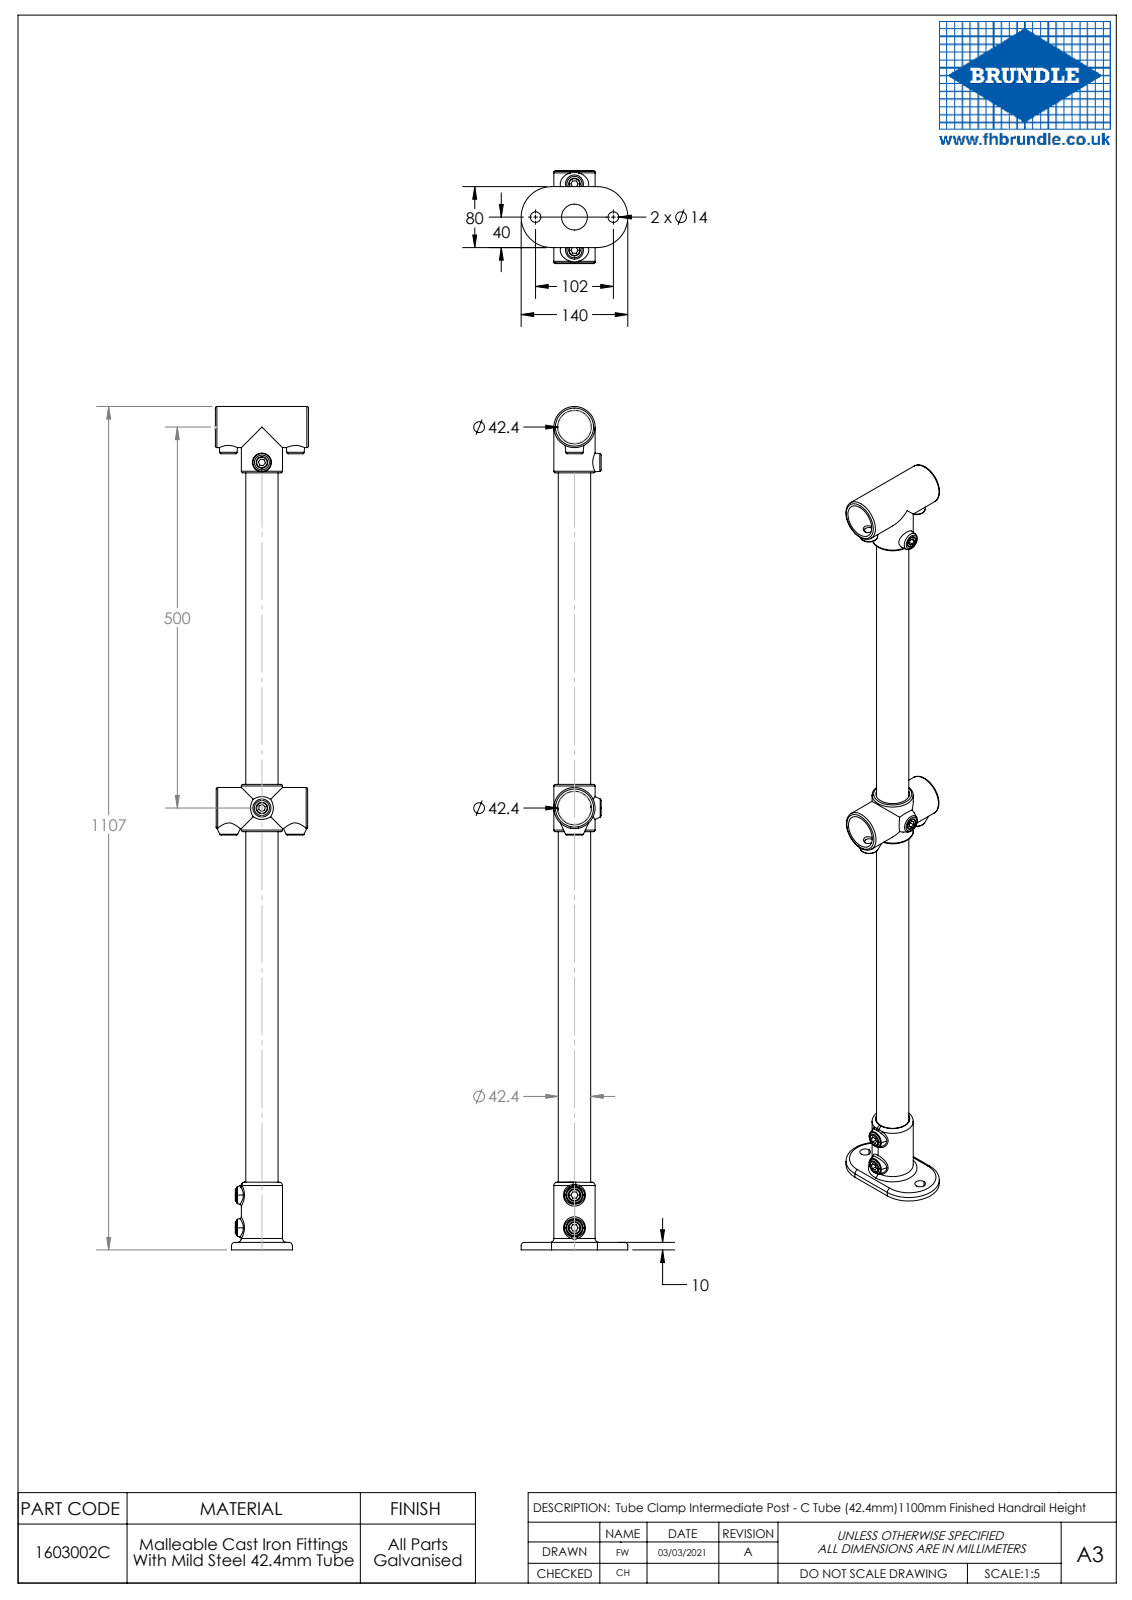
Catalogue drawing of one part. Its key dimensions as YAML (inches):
part_name: "16132C; Part2^1603002C_Default<As Machined>; 1603002C; 16119C (+2 more)"
step_written_by: "SolidWorks 2023 (AUTOMOTIVE_DESIGN)"
units: inches
bodies: {solids: 12, faces: 282, planar: 71, cylindrical: 54, other: 157}
overall_size: [43.583, 5.512, 4.803]
volume: 48.49
surface_area: 630.6
round_holes:
  - {diameter: 0.591, count: 5}
  - {diameter: 1.732, count: 3}
  - {diameter: 0.571, count: 1}
  - {diameter: 1.413, count: 1}
round_bosses_or_shafts:
  - {diameter: 0.63, count: 6}
  - {diameter: 2.126, count: 3}
  - {diameter: 1.669, count: 1}
face_to_face_distances: [0.039, 4.764, 19.705, 0.472, 0.315, 4.724, 18.72, 4.803, 0.177, 2.618]
hole_center_spacings: [0.02, 1.713, 1.732, 3.445, 3.425, 3.465, 17.857, 19.685]
